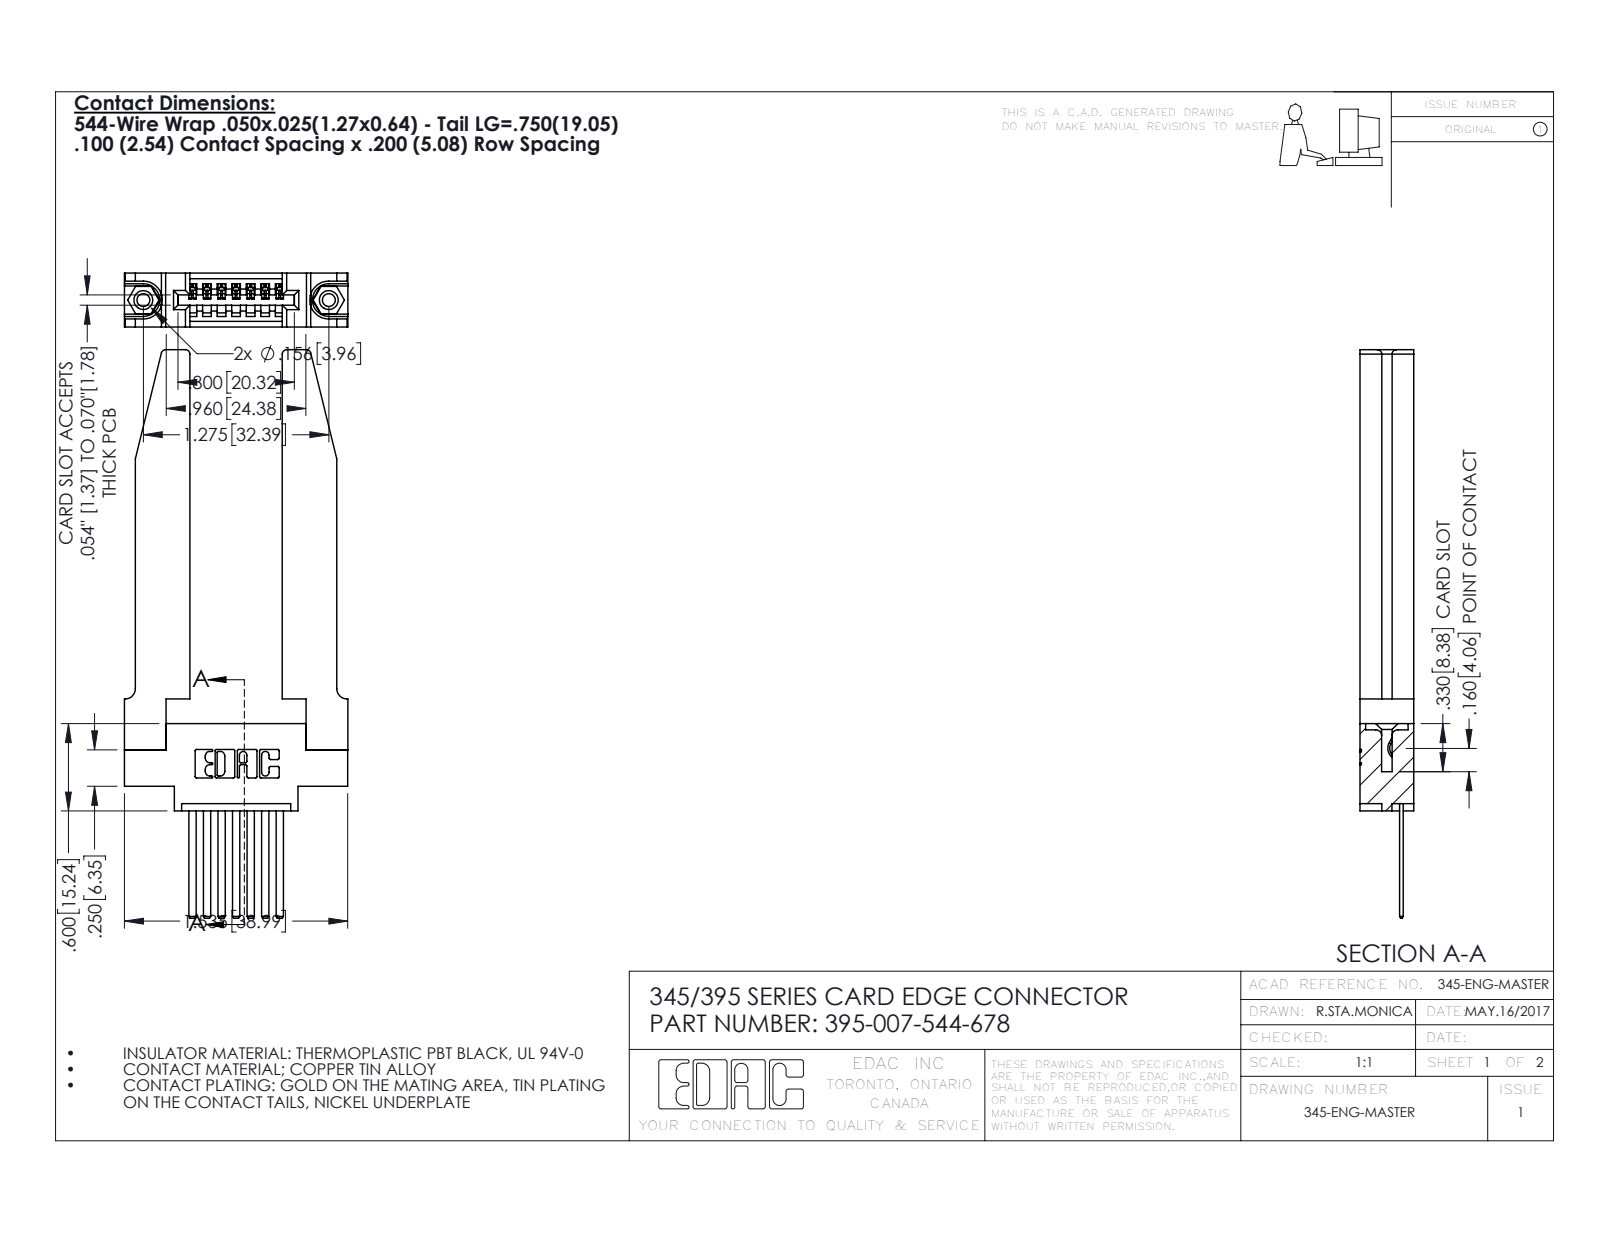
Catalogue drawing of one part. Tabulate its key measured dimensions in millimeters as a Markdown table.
| quantity | value |
| --- | --- |
| part name | 345-250-001_345-250-001-102; 345-292-001_345-293-144; 345 Part_0.170 Offset - 0.156 Dia-TH; 395-007-544-678 (+1 more) |
| STEP written by | SolidWorks 2016 (CONFIG_CONTROL_DESIGN) |
| units | millimeters |
| bodies | 12 solids, 728 faces (478 planar, 198 cylindrical, 52 other) |
| overall size | 99.2 × 39 × 9.4 |
| volume | 11 200 mm³ |
| surface area | 11 240 mm² |
| round holes (diameter × count) | 2.3 × 2, 3.2 × 2, 4 × 2, 1.6 × 1 |
| round bosses / shafts (diameter × count) | 3.9 × 2 |
| partial cylindrical surfaces (radius × count) | 0.3 × 22, 0.2 × 14, 0.8 × 8, 0.2 × 6, 0.8 × 6, 0.7 × 3, 0.8 × 2, 1 × 2 |
| main face-to-face distances | 9.4, 1.8, 7.6, 3.8, 5.6, 3.8, 16.1, 2, 2.5, 6.9 |
| hole center spacings | 6.9, 26.5, 32.4 |
